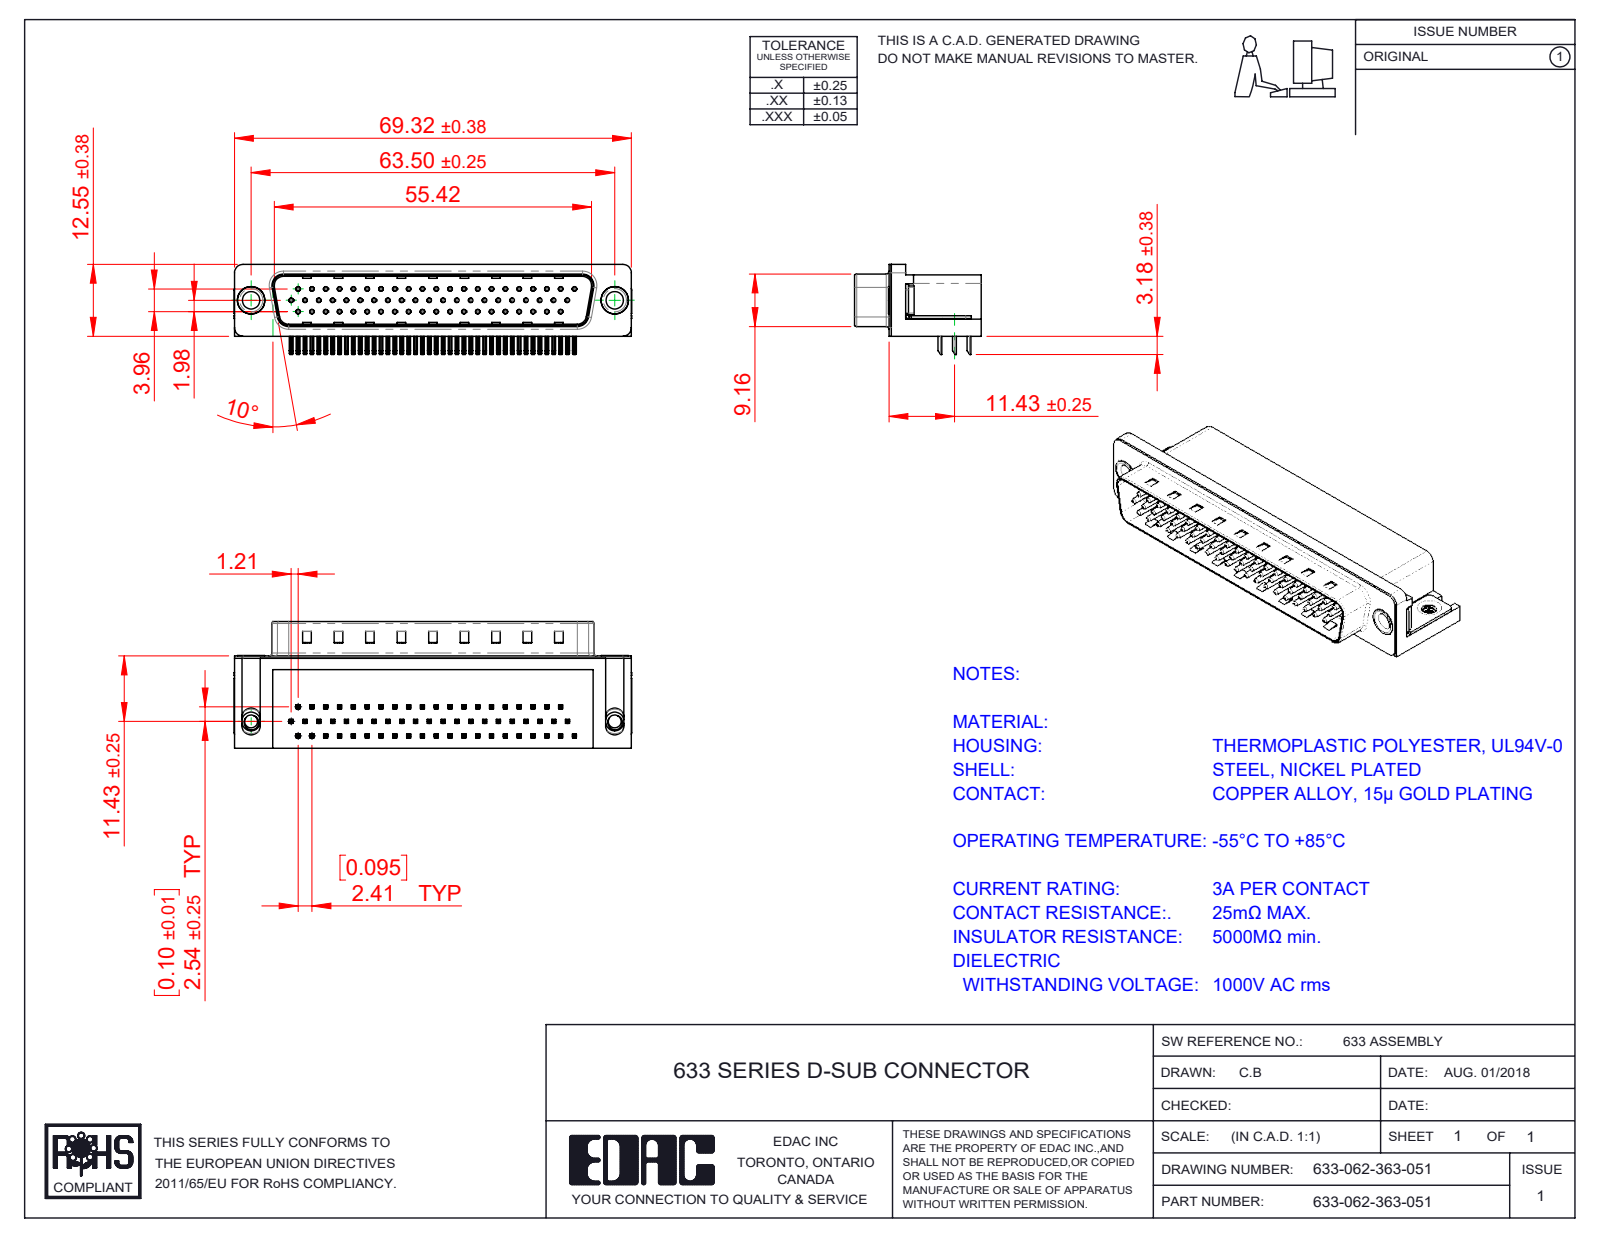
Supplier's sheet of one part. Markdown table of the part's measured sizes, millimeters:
| quantity | value |
| --- | --- |
| part name | 633-062-363-051; 633 Thru Hole Rivet; 633 Housing_62 Contact; 633 Contact Top (+4 more) |
| STEP written by | SolidWorks 2016 (CONFIG_CONTROL_DESIGN) |
| units | millimeters |
| bodies | 68 solids, 5066 faces (3213 planar, 1436 cylindrical, 417 other) |
| overall size | 69.4 × 22.1 × 15.73 |
| volume | 11 055 mm³ |
| surface area | 13 466 mm² |
| round holes (diameter × count) | 0.35 × 62, 0.8 × 62, 2.26 × 2, 3.05 × 2, 4 × 2, 4.8 × 2, 5 × 2 |
| round bosses / shafts (diameter × count) | 0.75 × 62, 4.9 × 2, 4.75 × 2, 3.85 × 2, 3.26 × 2 |
| partial cylindrical surfaces (radius × count) | 0.25 × 256, 0.12 × 124, 1 × 16, 0.5 × 9, 1.6 × 8, 1.5 × 7, 0.9 × 4, 2 × 4 |
| main face-to-face distances | 0.4, 10.35, 15.7, 8.76, 2.9, 2.5, 2.54, 8.36, 2.1, 10.46 |
| hole center spacings | 2.41, 4.82, 7.24, 9.65, 14.48, 16.89, 4.83, 7.23 |
